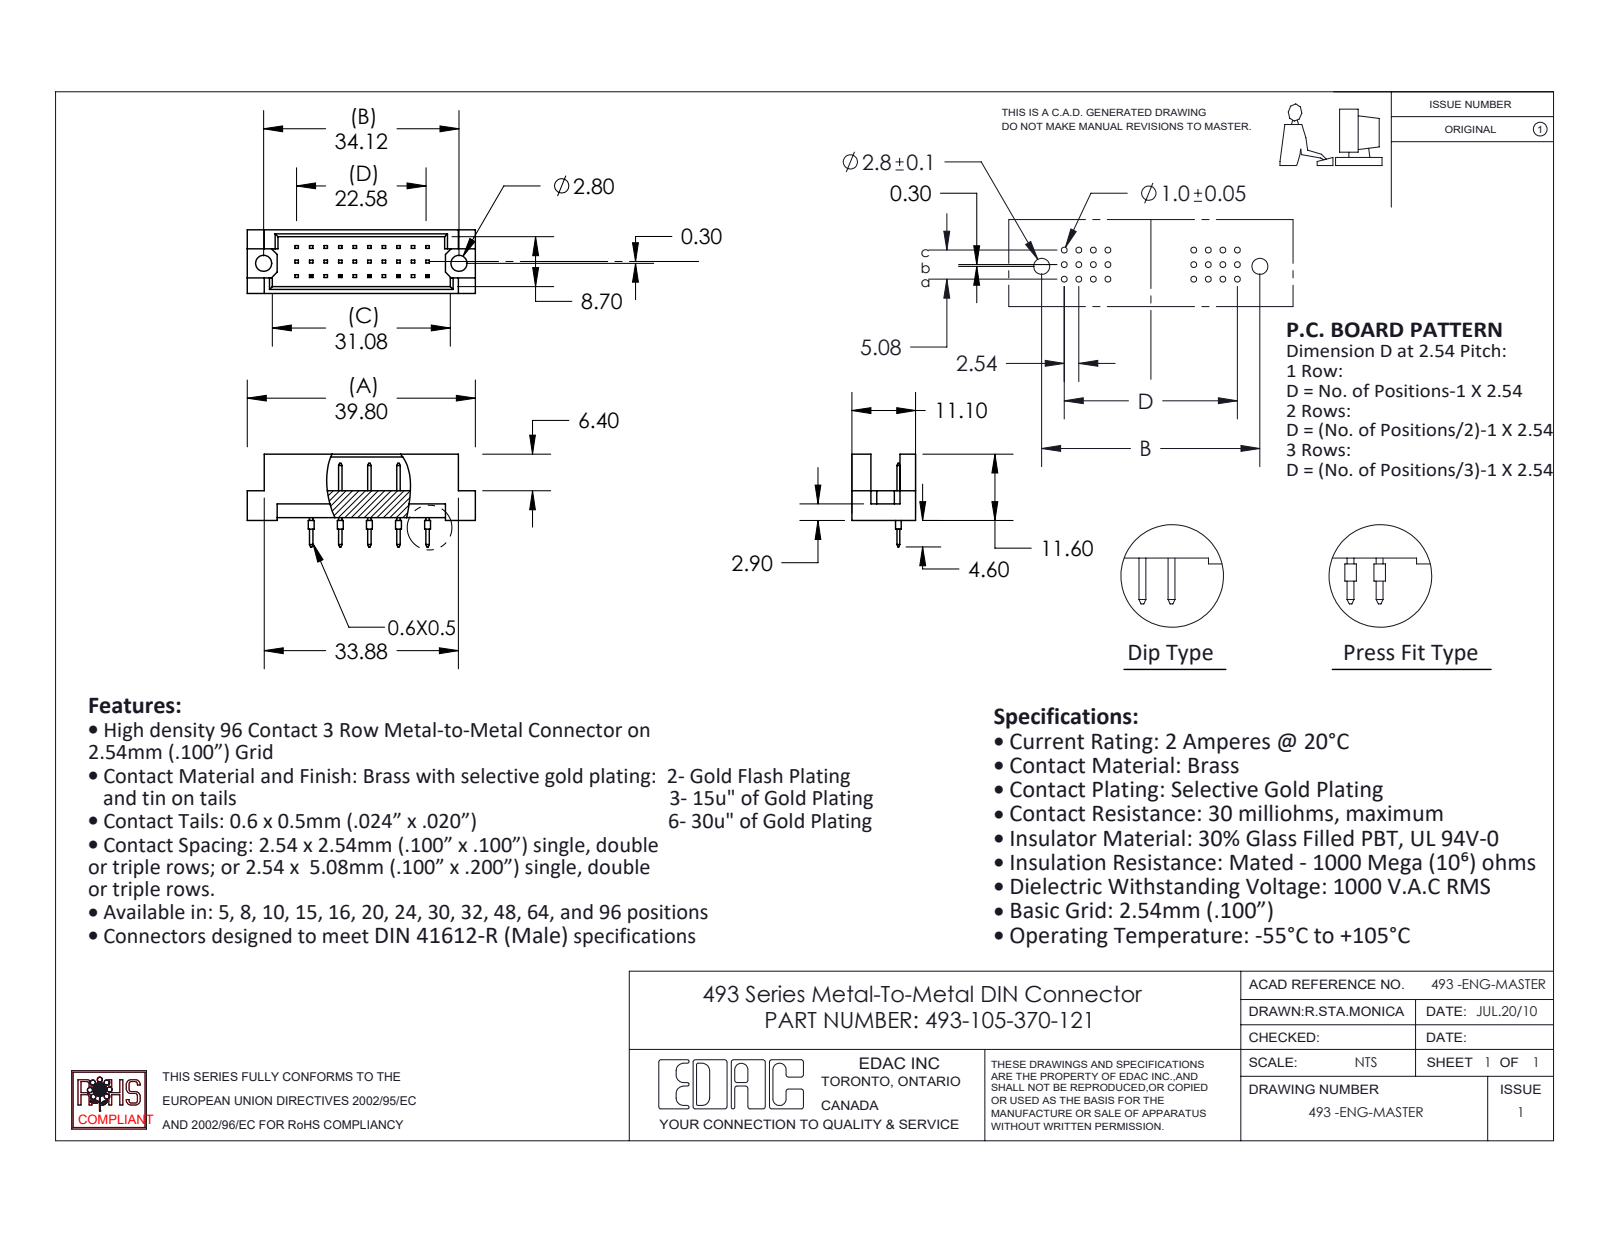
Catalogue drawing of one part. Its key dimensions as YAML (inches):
part_name: "493 Part_30; 493-105-370-121; 493-290_70"
step_written_by: "SolidWorks 2020 (CONFIG_CONTROL_DESIGN)"
units: inches
bodies: {solids: 6, faces: 282, planar: 268, cylindrical: 14, other: 0}
overall_size: [1.567, 0.638, 0.437]
volume: 0.146
surface_area: 4.507
round_holes:
  - {diameter: 0.11, count: 2}
round_bosses_or_shafts:
  - {diameter: 0.039, count: 5}
face_to_face_distances: [0.047, 0.39, 0.437, 0.343, 0.185, 0.02, 0.2, 0.094, 0.1, 0.091]
hole_center_spacings: [1.343]
